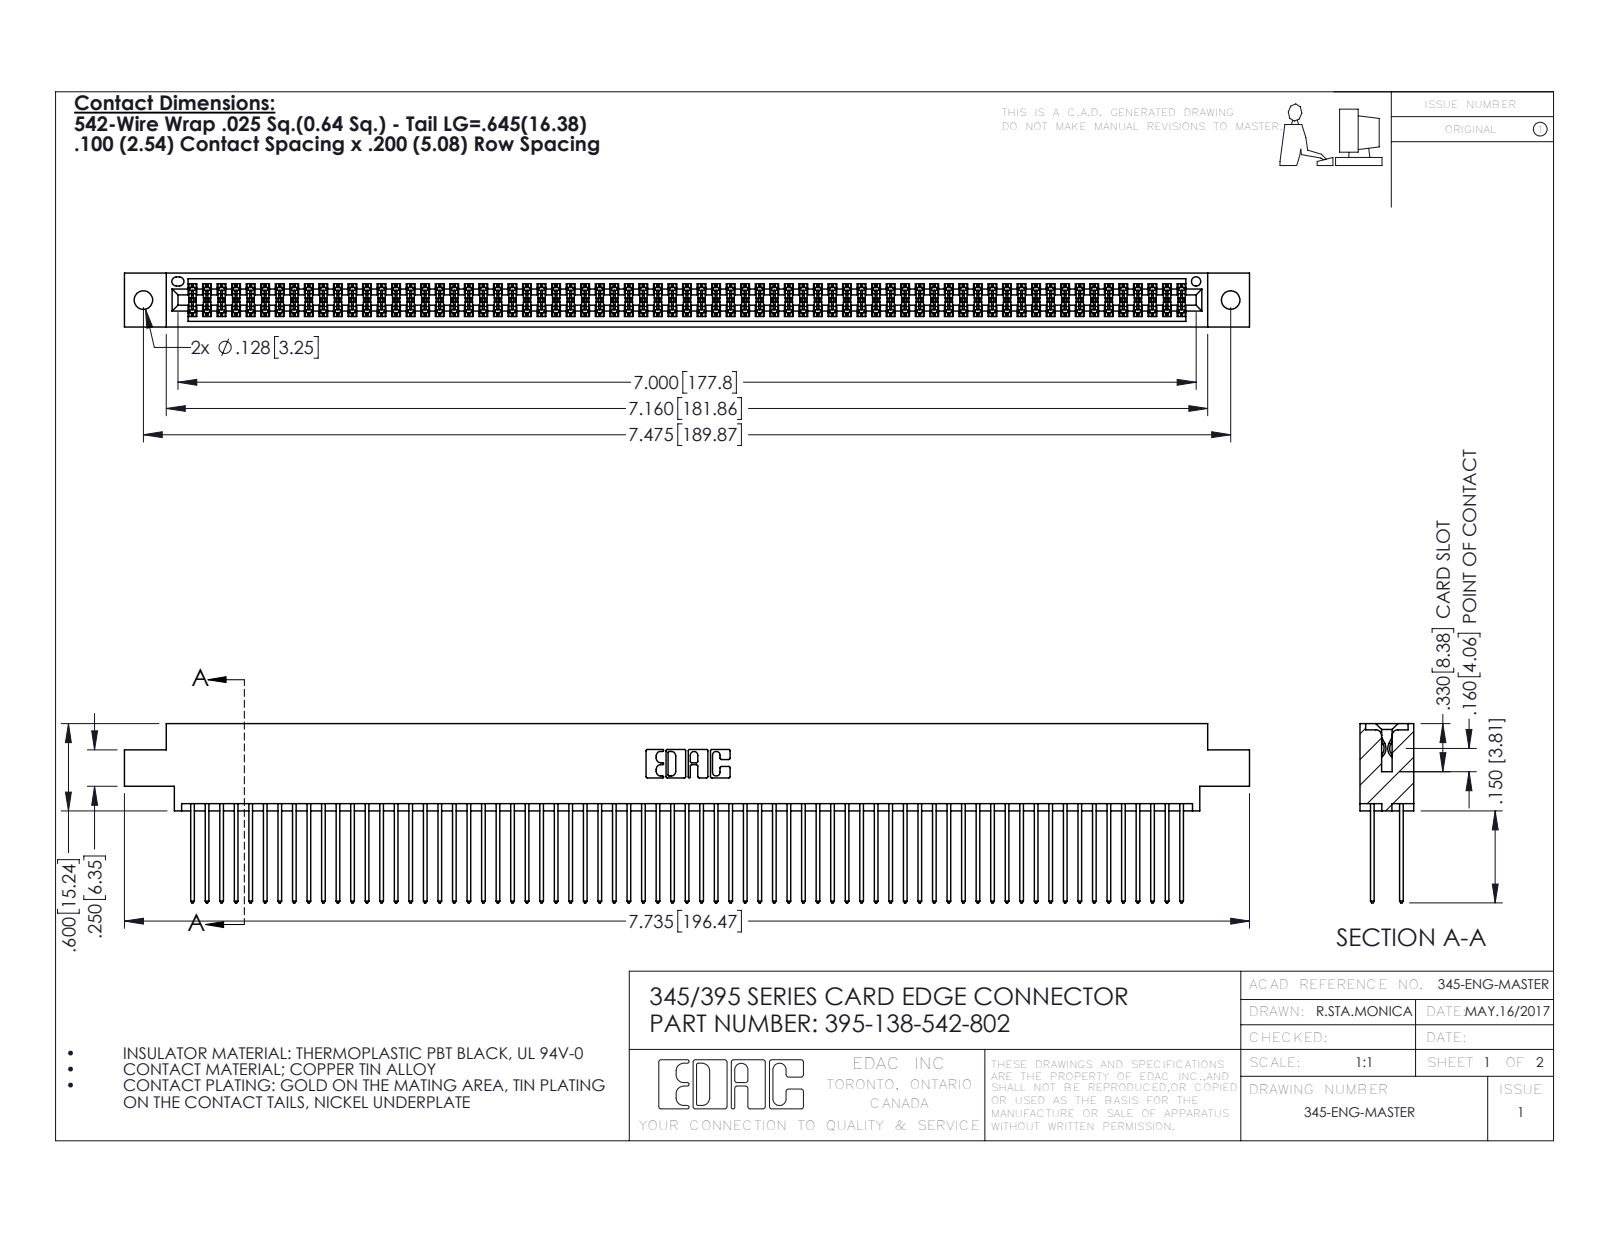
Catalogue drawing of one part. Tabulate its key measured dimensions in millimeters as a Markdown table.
| quantity | value |
| --- | --- |
| part name | 345-292-001_345-293-142; 345 Part_0.170 Offset - 0.128 Dia; 395-138-542-802 |
| STEP written by | SolidWorks 2016 (CONFIG_CONTROL_DESIGN) |
| units | millimeters |
| bodies | 139 solids, 7030 faces (4638 planar, 2392 cylindrical, 0 other) |
| overall size | 196.5 × 31.3 × 9.4 |
| volume | 19 830 mm³ |
| surface area | 32 710 mm² |
| round holes (diameter × count) | 3.3 × 2, 1.6 × 1 |
| partial cylindrical surfaces (radius × count) | 0.2 × 207, 0.3 × 138, 0.3 × 22, 0.2 × 6, 0.8 × 6, 0.7 × 3, 0.4 × 2, 0.5 × 2 |
| main face-to-face distances | 1.8, 7.6, 5.1, 2.5, 6.9, 0.6, 9.4, 5.7, 4.4, 3.8 |
| hole center spacings | 6.9, 183.9, 189.9 |
